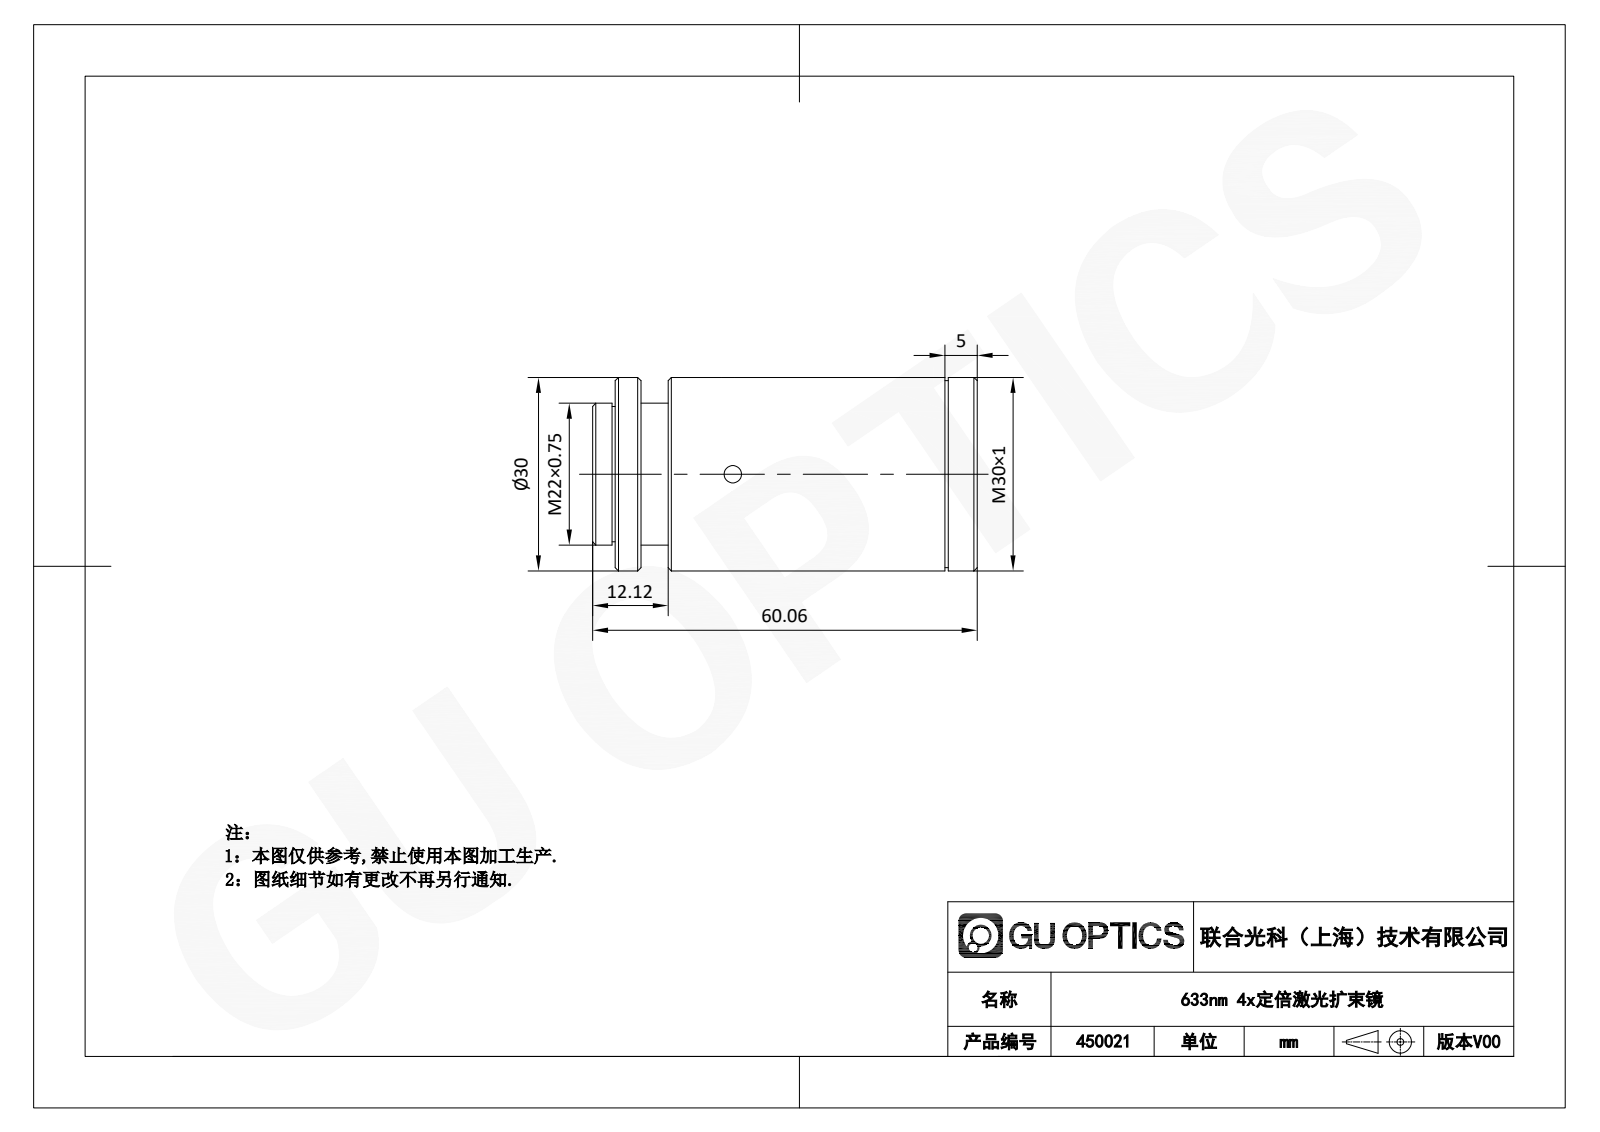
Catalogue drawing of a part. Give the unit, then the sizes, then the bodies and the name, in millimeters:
Units: millimetres
Overall size (bounding box): 60.06 × 30 × 30
Round holes (diameter × count): ⌀2 ×1, ⌀8 ×1, ⌀18 ×1, ⌀20 ×1
Round bosses / shafts (diameter × count): ⌀30 ×1, ⌀29 ×1, ⌀22 ×1, ⌀21 ×1
Main face-to-face distances: 2, 58.06, 1, 52.56, 1.5, 56.56, 2.5, 54.56, 3.5, 60.06
Volume: 38 785 mm³ · Surface area: 8 371 mm²
Bodies: 1 solid, 44 faces (12 planar, 22 cylindrical, 10 other)
Part name (STEP PRODUCT): 450021
STEP written by: SolidWorks 2020 (CONFIG_CONTROL_DESIGN)
